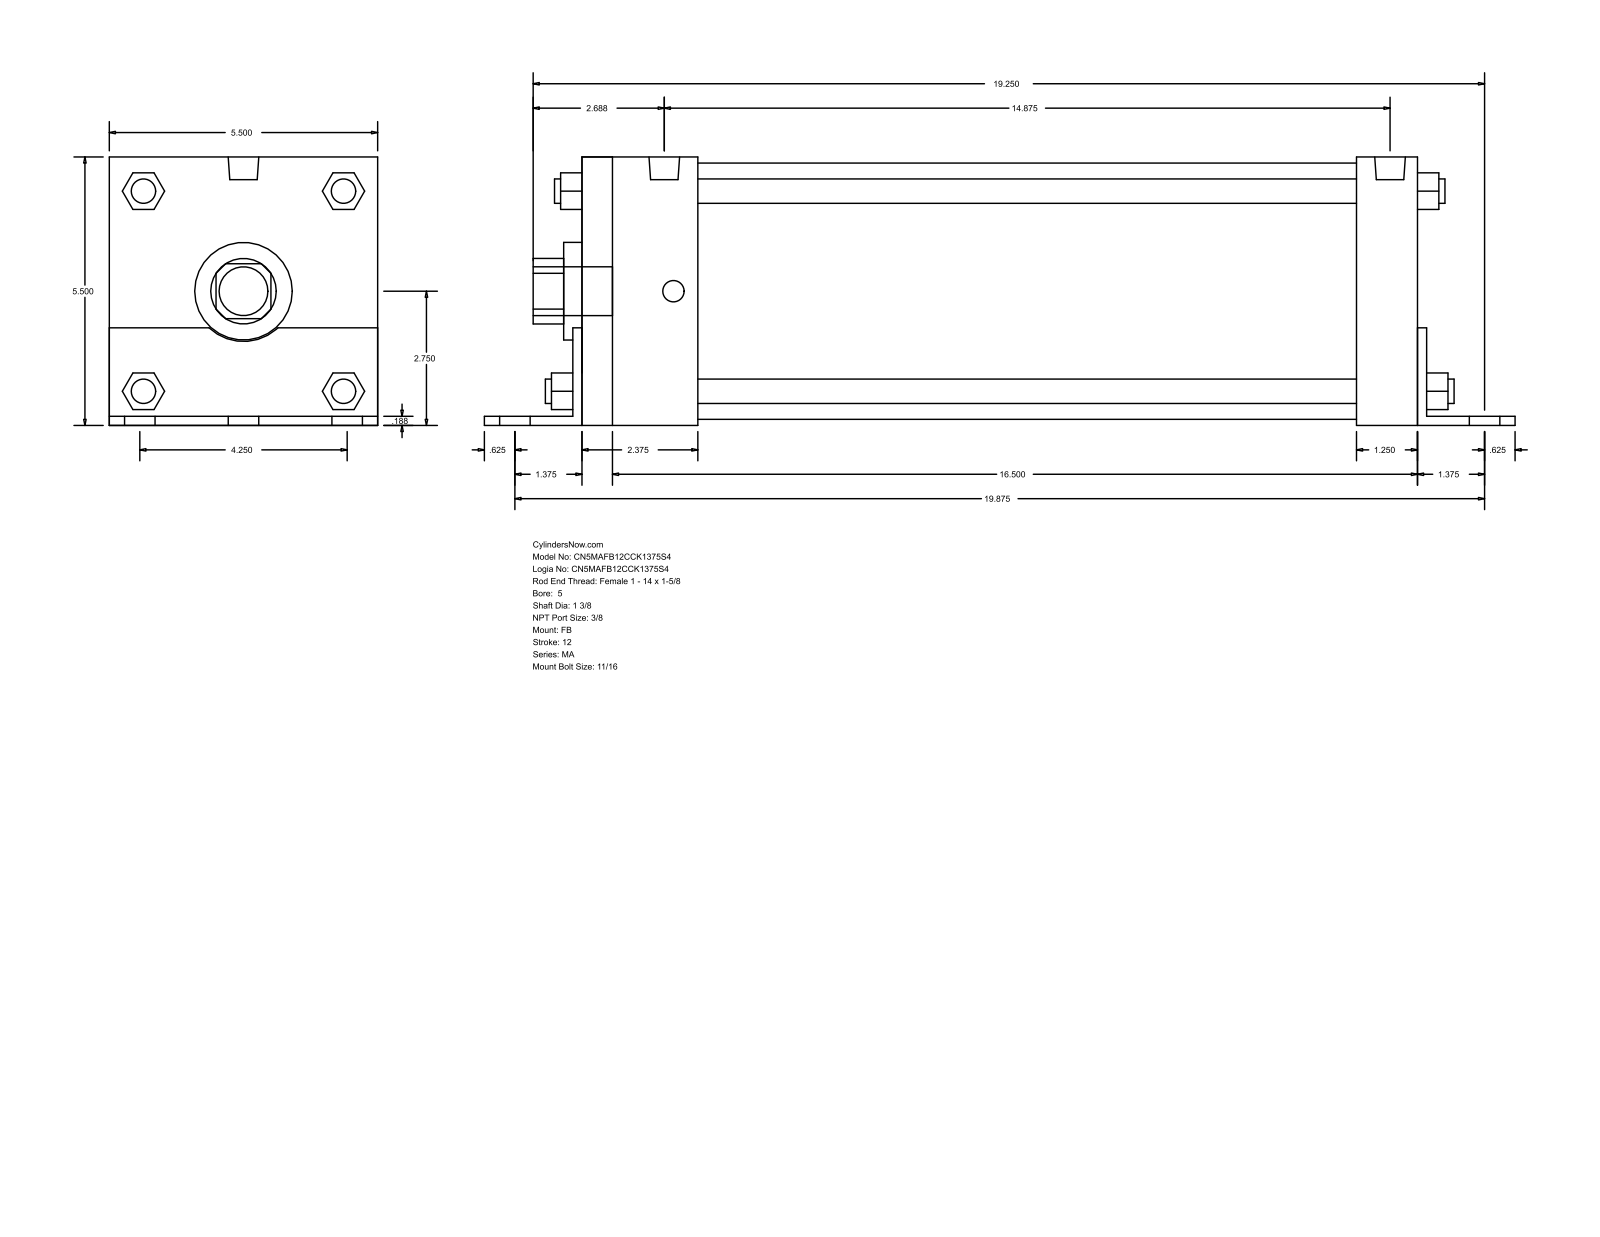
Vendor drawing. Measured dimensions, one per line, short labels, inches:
name: MA_FB__0500_1.375
written by: GSSL Pune (CONFIG_CONTROL_DESIGN)
unit: in
bodies: 0 solids, 140 faces (105 planar, 35 cylindrical, 0 other)
size: 21.125 × 5.502 × 5.5
holes: 1× ⌀1.375, 1× ⌀2, 1× ⌀5.25
bosses: 6× ⌀0.687, 4× ⌀0.5, 4× ⌀0.437, 2× ⌀0.627, 1× ⌀1
rounds: 1× R0.672, 1× R1.03
face distances: 5.5, 0.187, 5.502, 17.313, 0.185, 5.315, 17.125, 17.5, 1.438, 2.562
